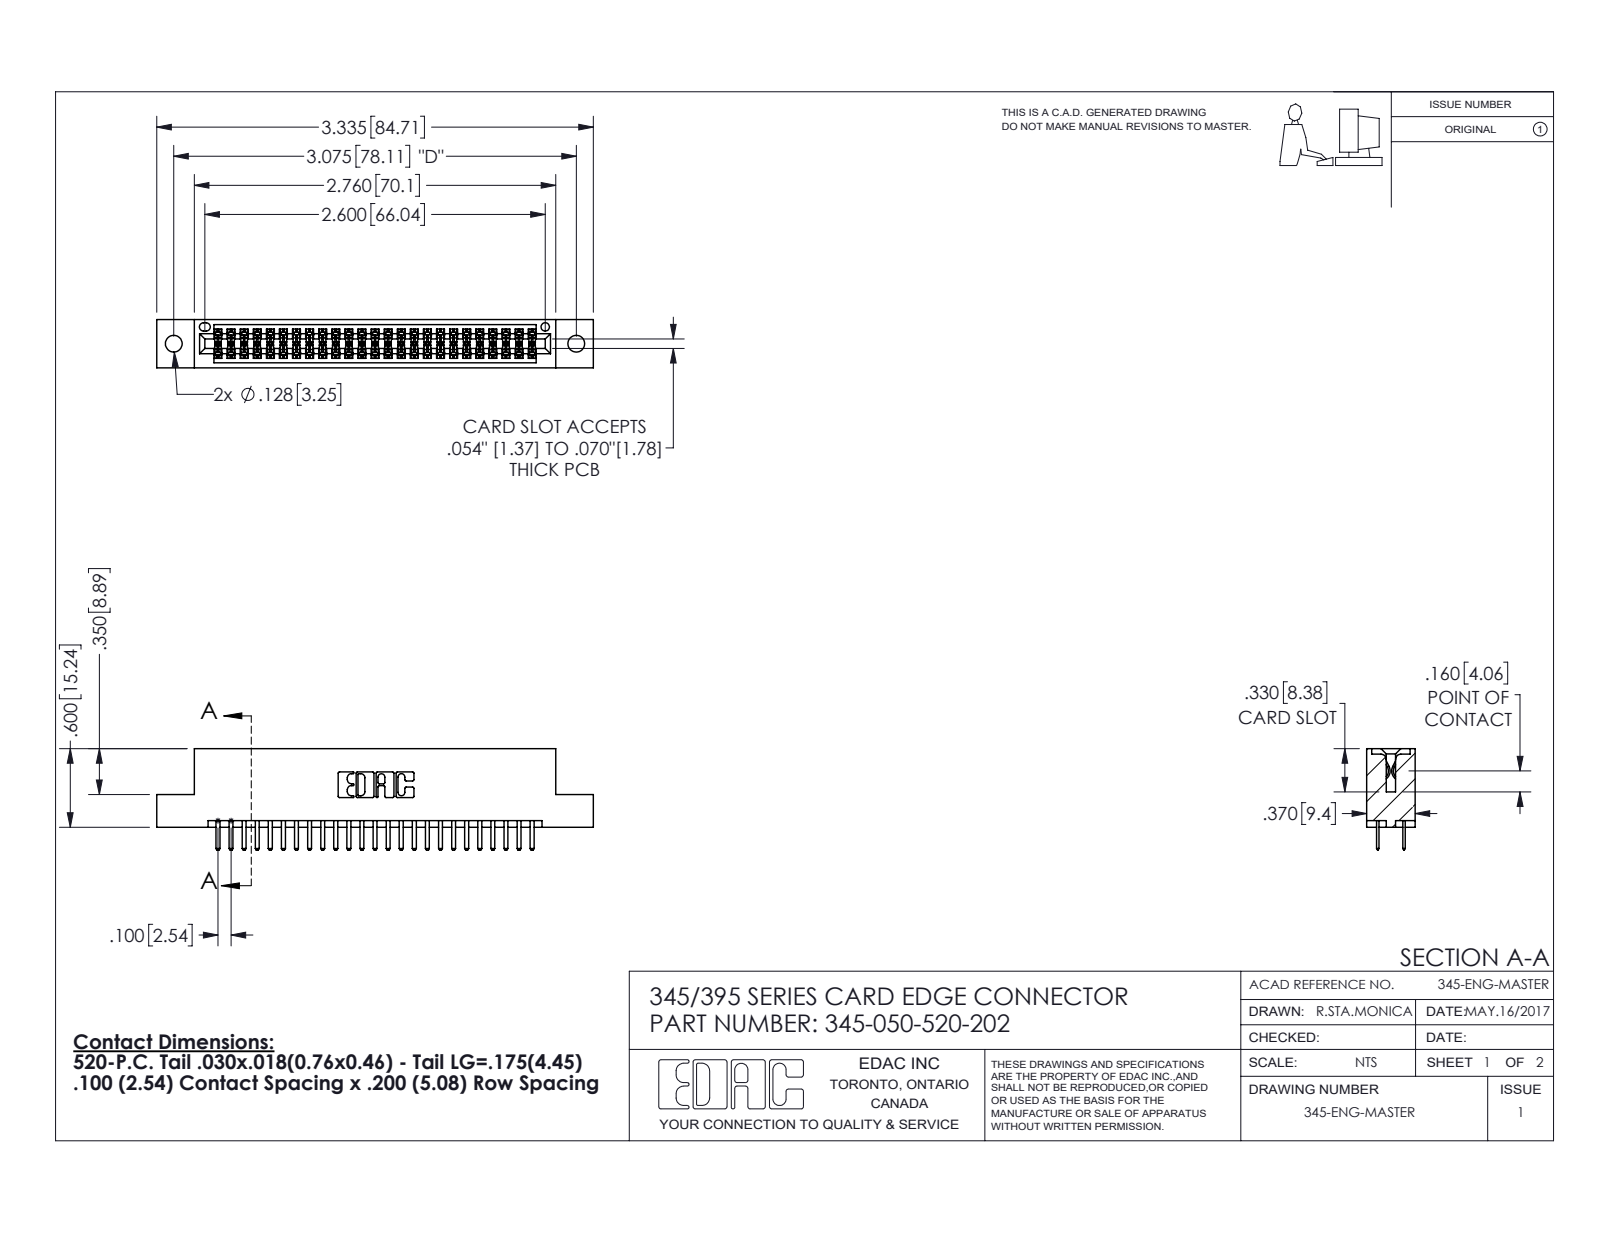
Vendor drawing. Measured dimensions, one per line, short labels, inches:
name: 345-050-520-202; 345-292-001_345-293-120; 345 Part_Flush Mounting Lugs - 0.128 Dia
written by: SolidWorks 2016 (CONFIG_CONTROL_DESIGN)
unit: in
bodies: 51 solids, 2826 faces (1830 planar, 996 cylindrical, 0 other)
size: 3.335 × 0.775 × 0.37
volume: 0.489 in³; area: 17.35 in²
holes: 2× ⌀0.128, 1× ⌀0.064
rounds: 75× R0.006, 54× R0.01, 22× R0.01, 6× R0.007, 6× R0.031, 3× R0.026, 2× R0.014, 2× R0.019
face distances: 0.298, 0.072, 0.2, 0.37, 0.098, 0.272, 0.025, 0.225, 0.022, 0.072
hole spacings: 0.27, 2.84, 3.075
